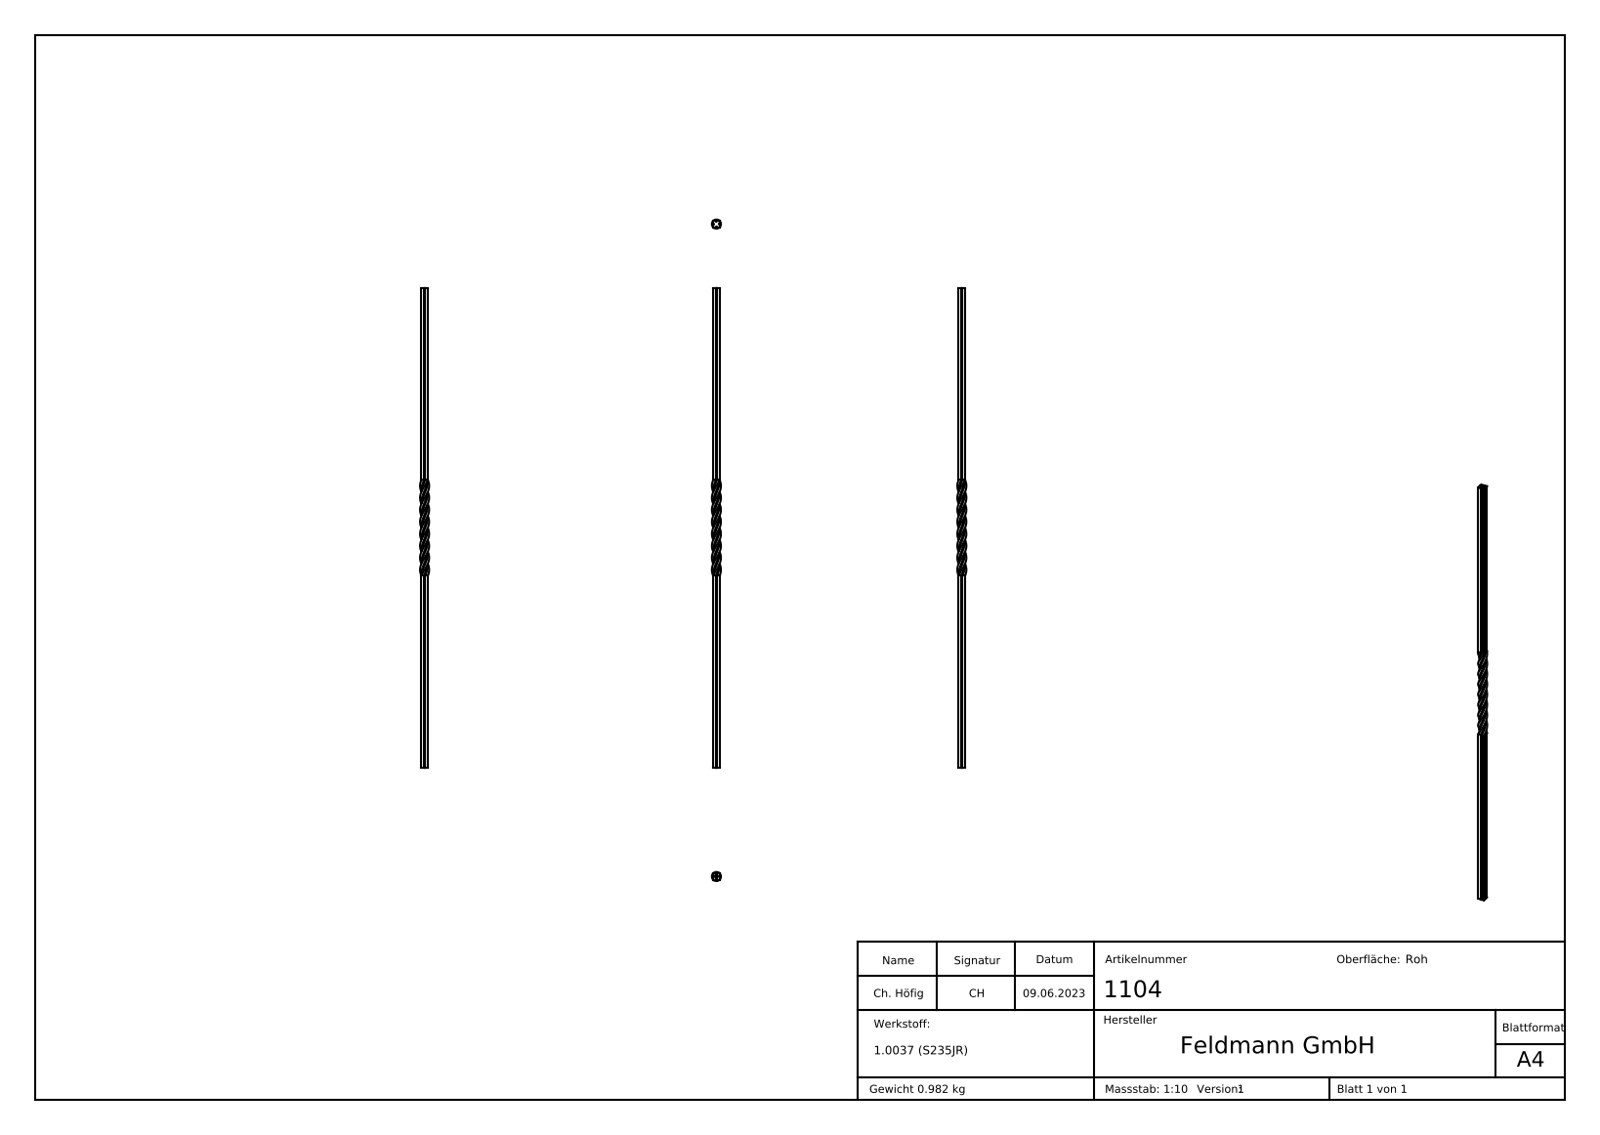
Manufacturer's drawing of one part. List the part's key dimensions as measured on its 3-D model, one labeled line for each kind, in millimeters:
Part name (STEP PRODUCT): 1104
STEP written by: SolidWorks 2018 (CONFIG_CONTROL_DESIGN)
Units: millimetres
Bodies: 1 solid, 246 faces (153 planar, 0 cylindrical, 93 other)
Overall size (bounding box): 900 × 16.97 × 16.97
Volume: 125 867 mm³ · Surface area: 46 775 mm²
Main face-to-face distances: 12, 7.08, 900, 899.9, 1.76, 1.62, 5, 7, 2.32, 0.54
